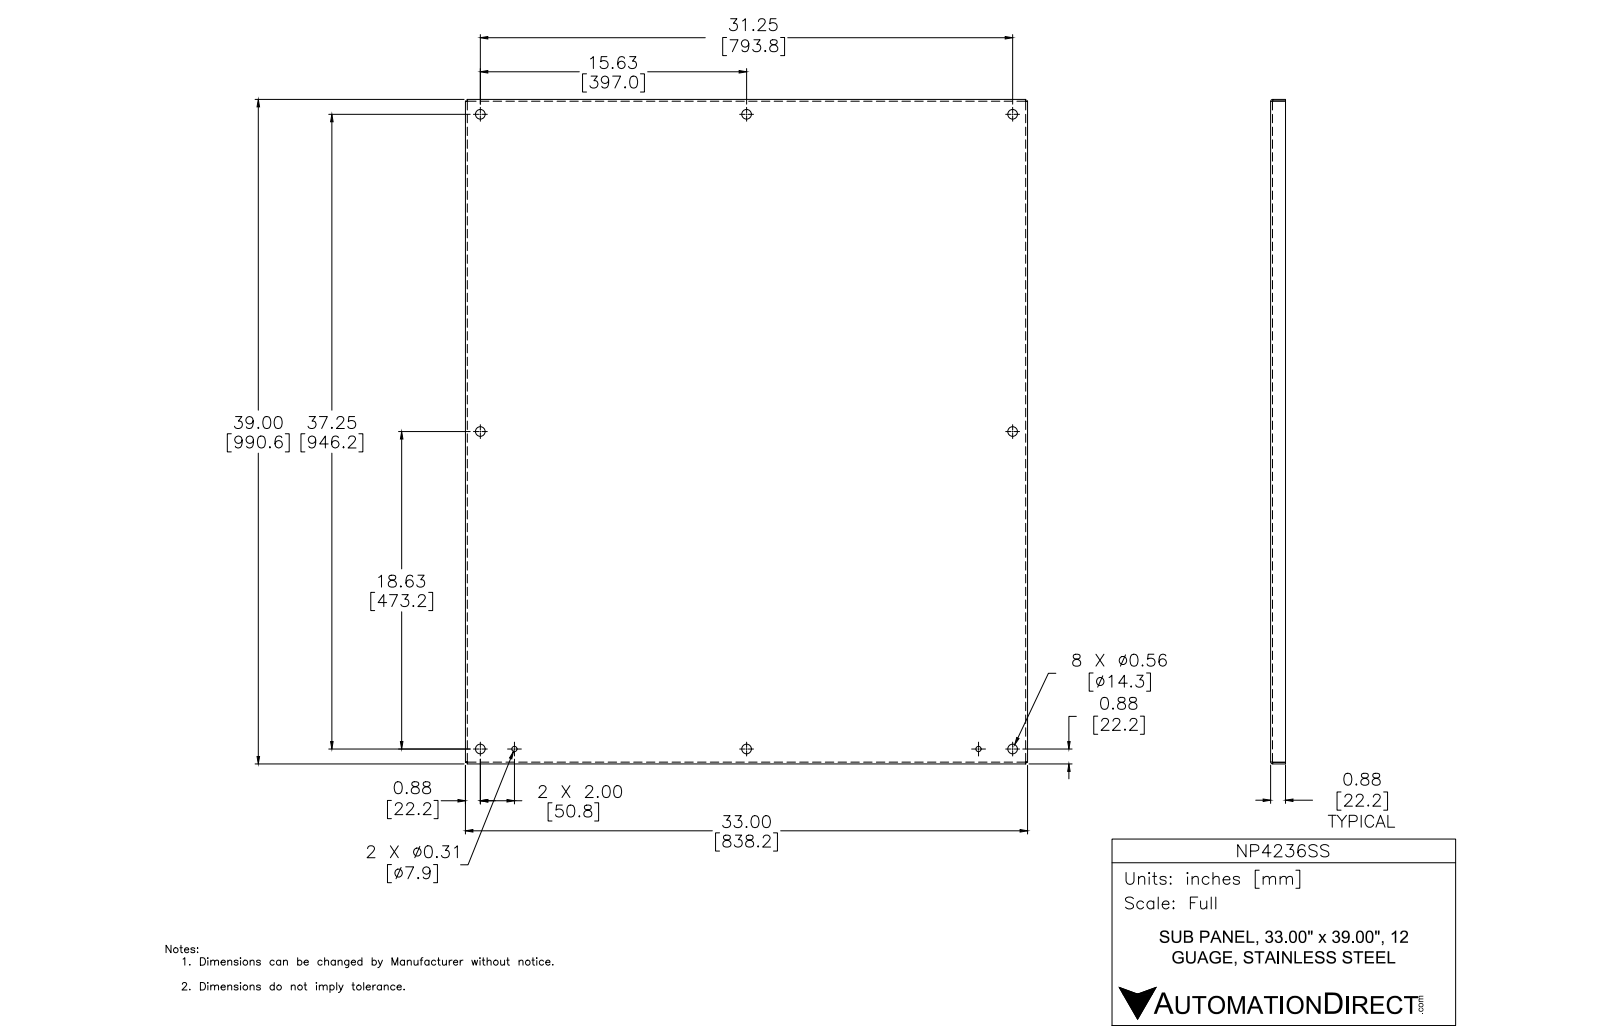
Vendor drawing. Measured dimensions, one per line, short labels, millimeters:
name: NP4236SS
written by: Autodesk Inventor 2012 (AUTOMOTIVE_DESIGN)
unit: mm
bodies: 1 solid, 48 faces (22 planar, 18 cylindrical, 8 other)
size: 990.6 × 838.2 × 22.2
volume: 2 137 000 mm³; area: 1 806 000 mm²
holes: 8× ⌀14.3, 2× ⌀7.9
rounds: 4× R0.8, 4× R3.2
face distances: 2.4, 835.8, 988.2, 838.2, 833.5, 990.6, 985.9, 19.8, 22.2, 2.7
hole spacings: 946.2, 346.1, 396.9, 396.9, 473.1, 473.1, 475.8, 617.5
